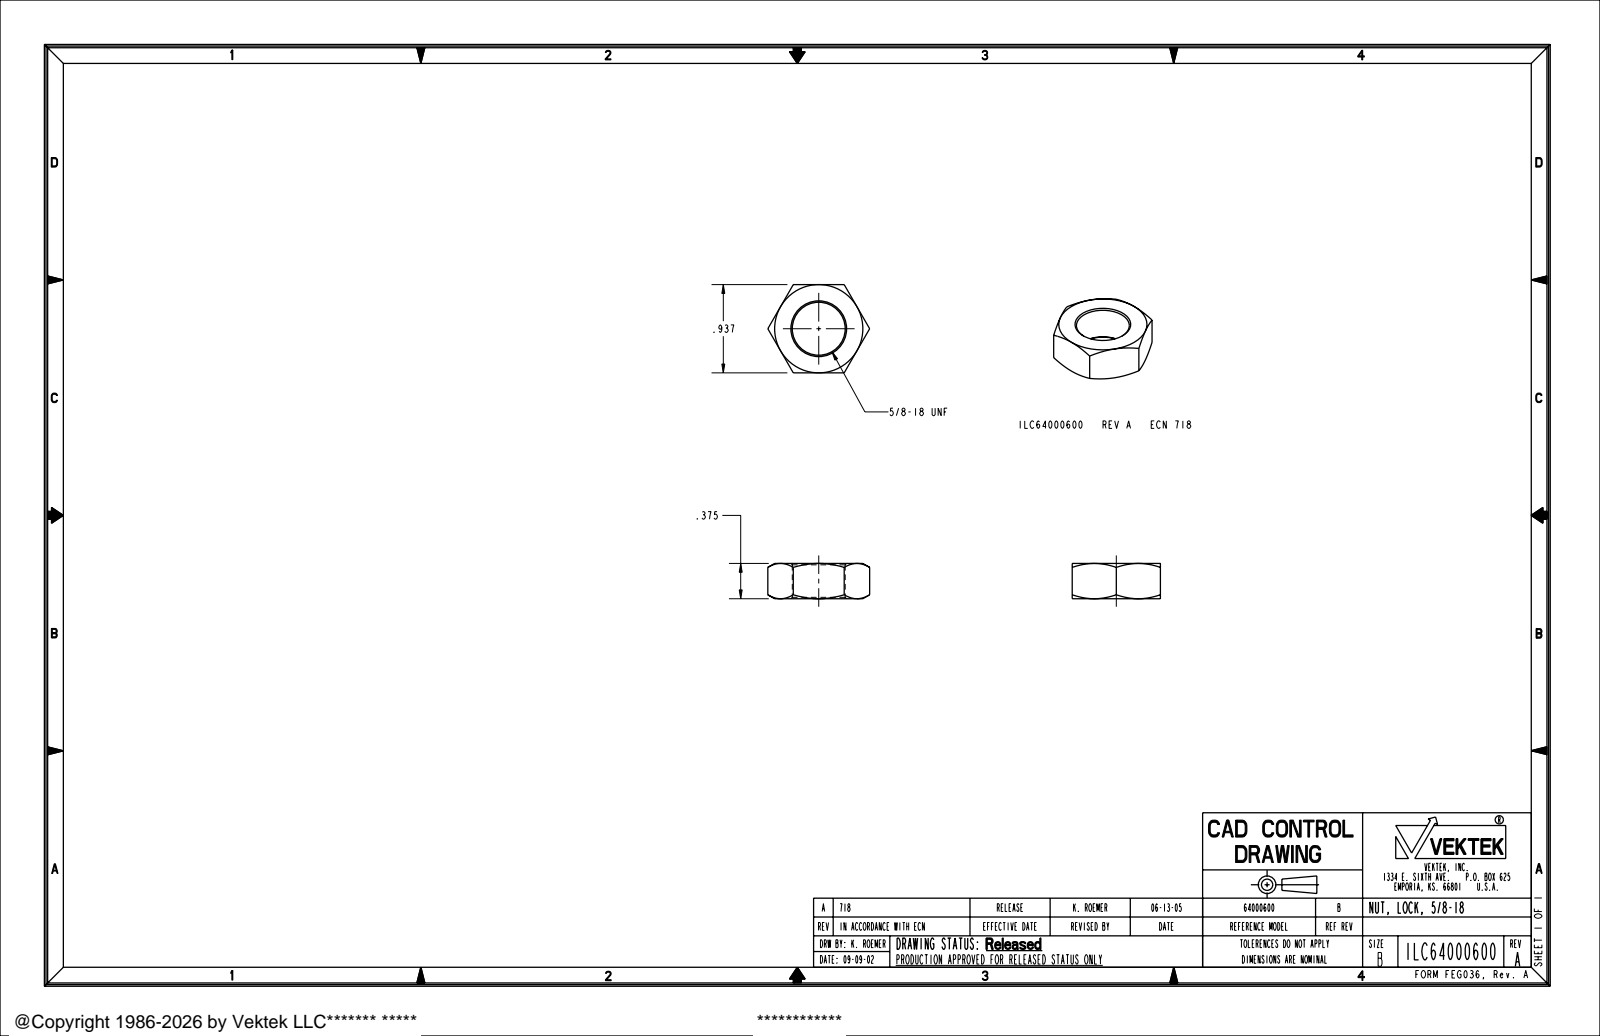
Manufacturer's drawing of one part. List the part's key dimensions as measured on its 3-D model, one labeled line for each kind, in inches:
Part name (STEP PRODUCT): ILC64000600
STEP written by: PRO/ENGINEER BY PARAMETRIC TECHNOLOGY CORPORATION, 2004290 (AUTOMOTIVE_DESIGN_CC2)
Units: inches
Bodies: 1 solid, 26 faces (8 planar, 2 cylindrical, 16 other)
Overall size (bounding box): 1.082 × 0.937 × 0.375
Volume: 0.19 in³ · Surface area: 2.802 in²
Round holes (diameter × count): ⌀0.562 ×1
Main face-to-face distances: 0.937, 0.375
